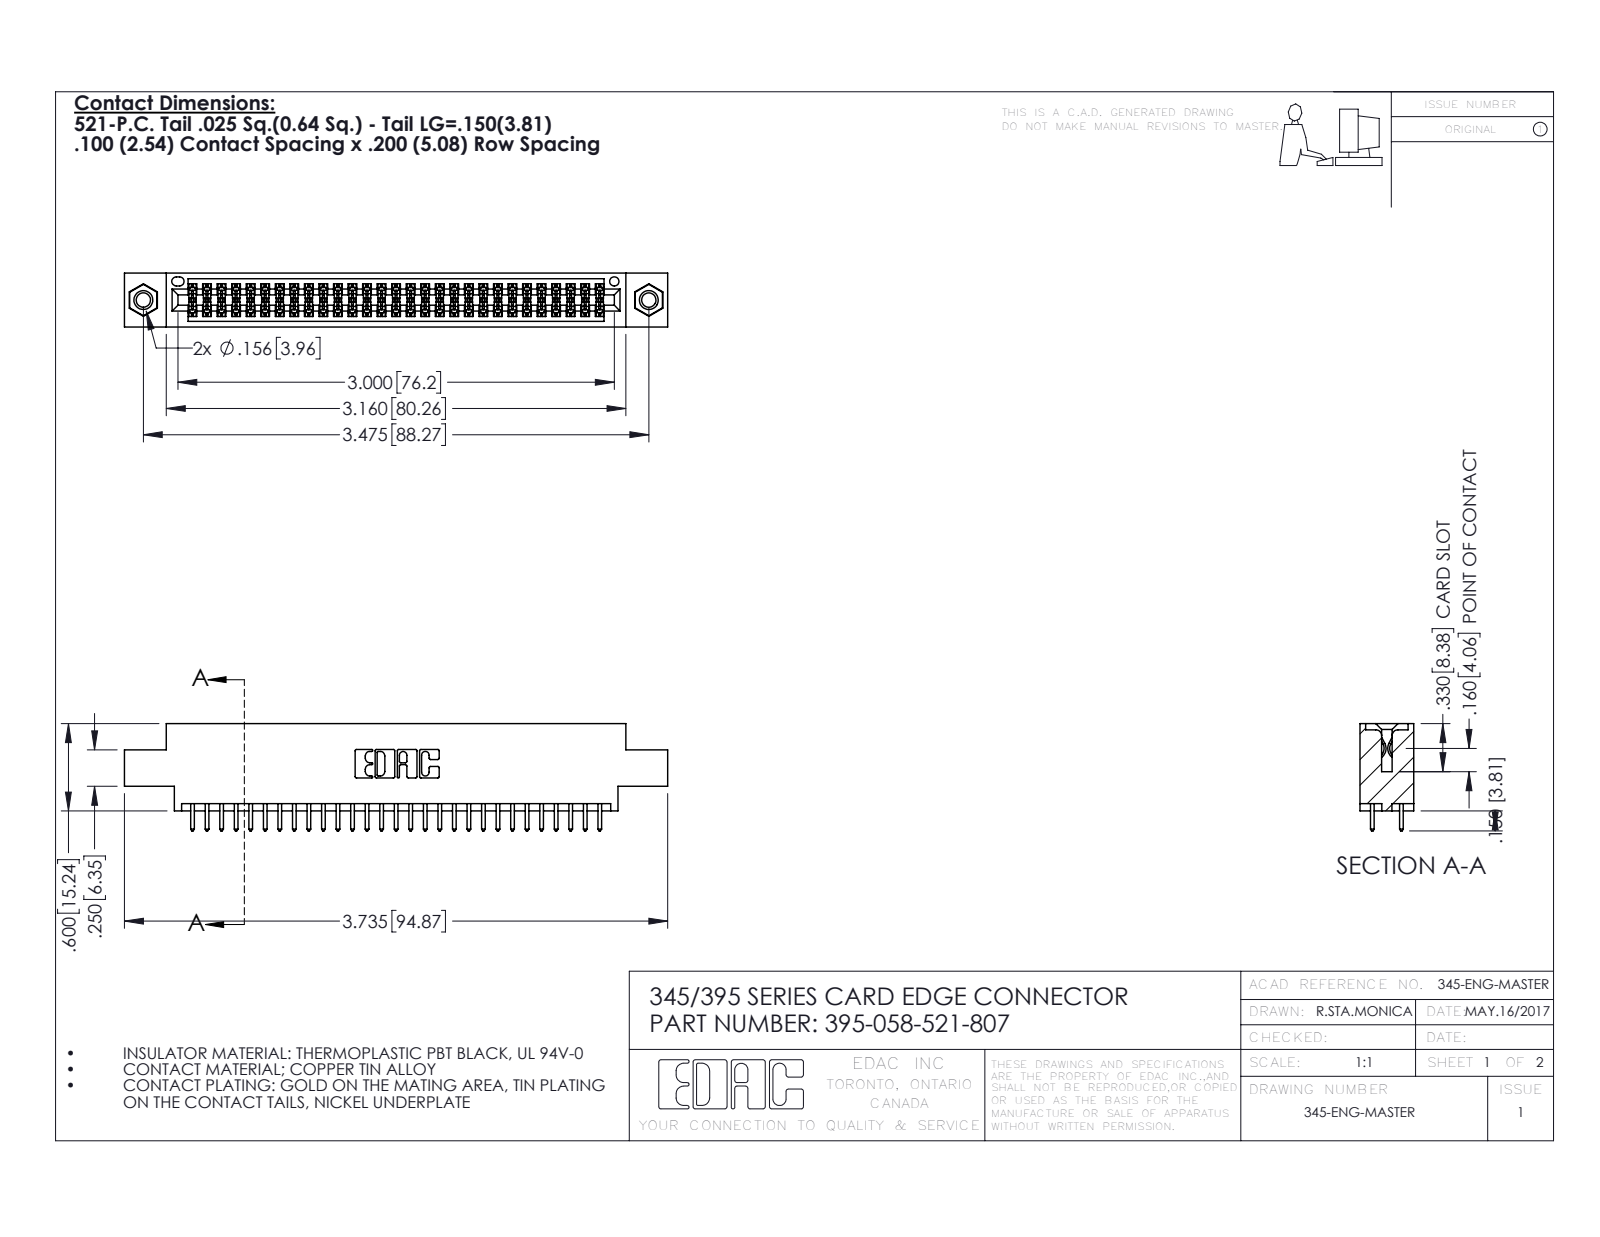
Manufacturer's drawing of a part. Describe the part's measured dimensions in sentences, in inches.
The part is named "345-292-001_345-293-121; 395-058-521-807; 345 Part_0.170 Offset - 0.156 Dia-TI; 345-250-001_345-250-005-103". Its 3-D file was written by "SolidWorks 2016 (CONFIG_CONTROL_DESIGN)". It is 61 solids with 3090 faces: 2030 planar, 1044 cylindrical and 16 other. Overall it measures 3.735 by 0.737 by 0.37 inches. Its volume is 0.546 cubic inches and its surface area 20.13 square inches. Round holes: 2 of diameter 0.098, 2 of diameter 0.125, 2 of diameter 0.156, 1 of diameter 0.064. Round bosses or shafts: 2 of diameter 0.155. Partial cylindrical surfaces (rounded edges, fillets, slot ends): 87 of radius 0.006, 58 of radius 0.01, 22 of radius 0.01, 6 of radius 0.007, 6 of radius 0.031, 3 of radius 0.026, 2 of radius 0.014, 2 of radius 0.019. The main face-to-face distances are 0.072, 0.298, 0.37, 0.2, 0.098, 0.272, 0.025, 0.225, 0.175, 0.149. The hole center spacings are 0.27, 3.24, 3.475.
